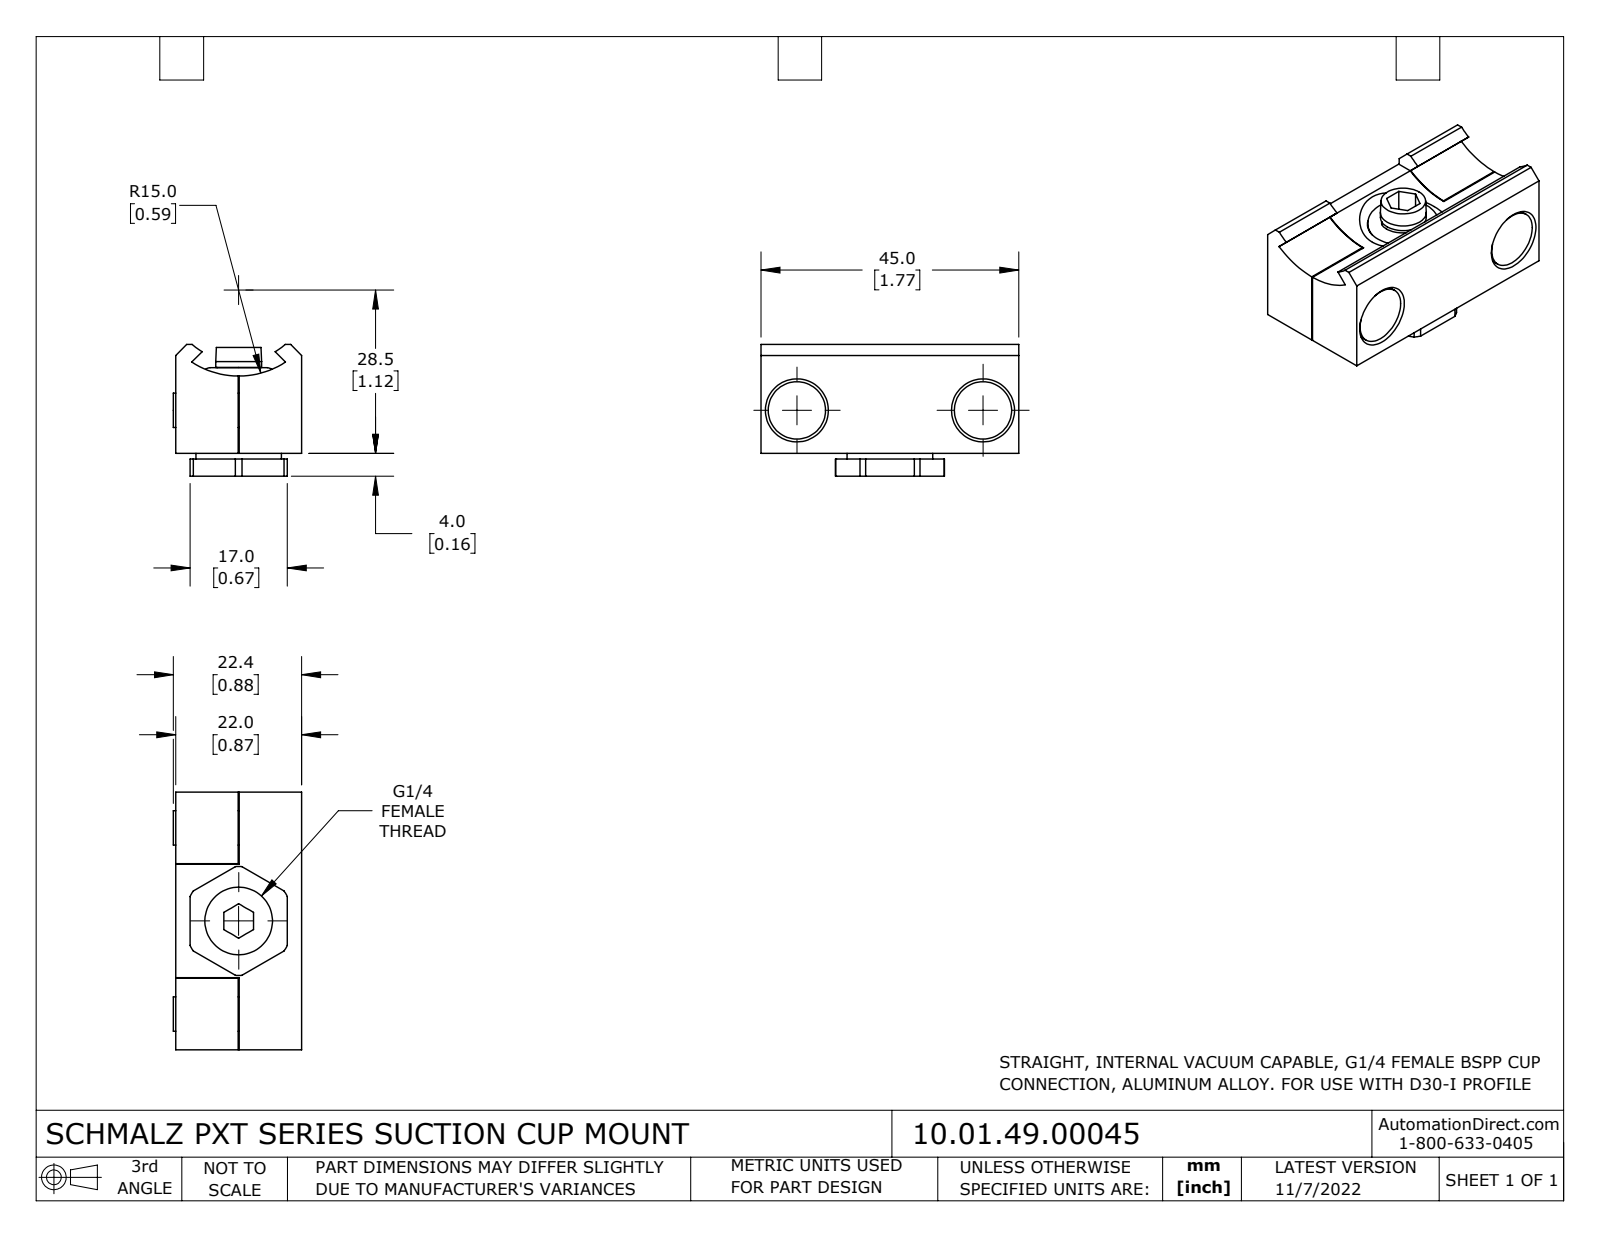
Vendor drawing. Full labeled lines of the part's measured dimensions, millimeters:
Part name (STEP PRODUCT): 10.01.49.00045
STEP written by: SolidWorks 2021 (CONFIG_CONTROL_DESIGN)
Units: millimetres
Bodies: 7 solids, 112 faces (55 planar, 45 cylindrical, 12 other)
Overall size (bounding box): 45 × 23 × 22.4
Volume: 14 942 mm³ · Surface area: 10 754 mm²
Round holes (diameter × count): ⌀5 ×2, ⌀6.6 ×2, ⌀11 ×2, ⌀11.8 ×1, ⌀15.25 ×1
Round bosses / shafts (diameter × count): ⌀10 ×2, ⌀6 ×2, ⌀16.66 ×1, ⌀14.95 ×1, ⌀8 ×1, ⌀7.5 ×1
Partial cylindrical surfaces — rounded edges, fillets, slot ends (radius × count): R9.5 ×1, R12.5 ×1, R15 ×1
Main face-to-face distances: 11.1, 22, 10.9, 12.6, 19.9, 12.5, 32.5, 45, 32.4, 6.4
Hole centre spacings: 32.5
